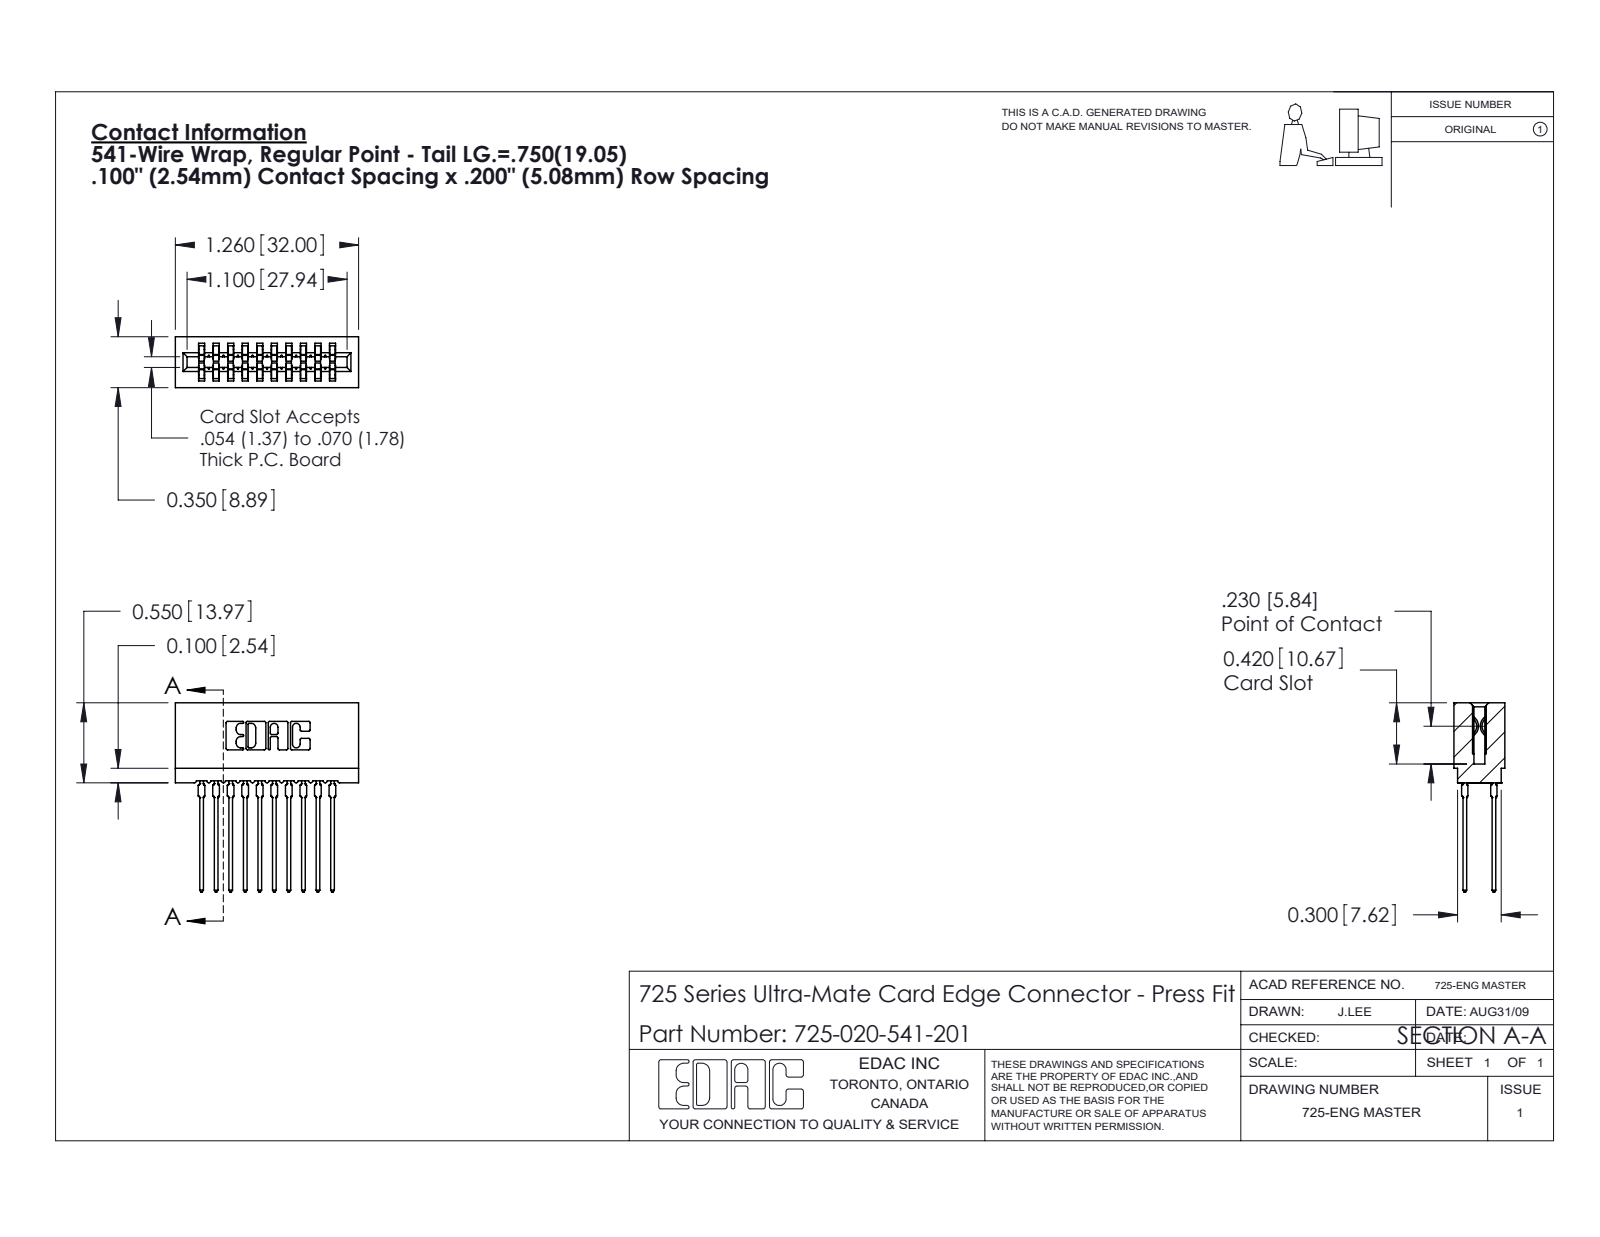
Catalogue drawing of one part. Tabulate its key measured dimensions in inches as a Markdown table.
| quantity | value |
| --- | --- |
| part name | 725-020-541-201; 745-292-001_541; 725 Part_Insulator Option - 01 |
| STEP written by | SolidWorks 2020 (CONFIG_CONTROL_DESIGN) |
| units | inches |
| bodies | 21 solids, 1885 faces (975 planar, 390 cylindrical, 520 other) |
| overall size | 1.301 × 1.26 × 0.35 |
| volume | 0.171 in³ |
| surface area | 8.709 in² |
| partial cylindrical surfaces (radius × count) | 0.021 × 40, 0.01 × 22, 0.015 × 20, 0.005 × 8, 0.011 × 8, 0.007 × 6, 0.031 × 6, 0.026 × 3 |
| main face-to-face distances | 0.2, 0.1, 0.3, 0.4, 0.042, 0.5, 0.142, 0.058, 0.063, 0.287 |
